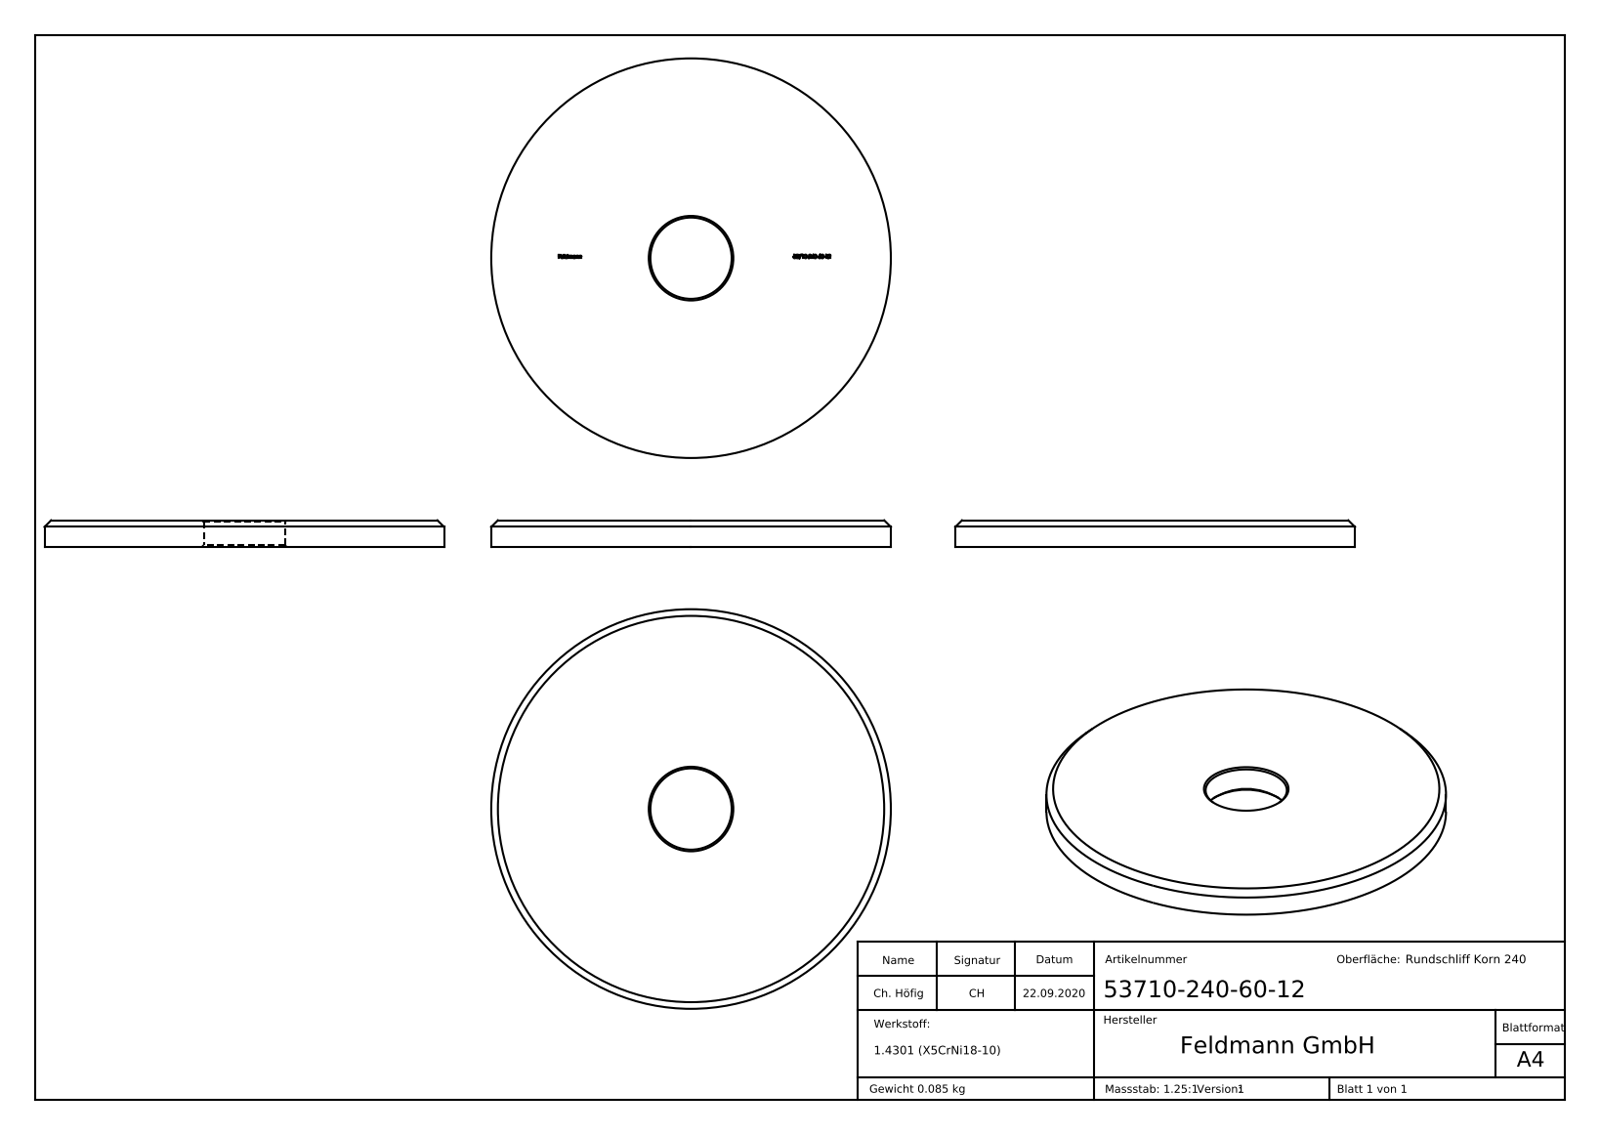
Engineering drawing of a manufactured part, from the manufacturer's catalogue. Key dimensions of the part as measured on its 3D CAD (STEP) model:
Part name (STEP PRODUCT): 53710-240-60-12
STEP written by: SolidWorks 2018 (CONFIG_CONTROL_DESIGN)
Units: millimetres
Bodies: 1 solid, 282 faces (154 planar, 4 cylindrical, 124 other)
Overall size (bounding box): 60 × 60 × 4
Volume: 10 746 mm³ · Surface area: 6 210 mm²
Round holes (diameter × count): ⌀12.2 ×1
Round bosses / shafts (diameter × count): ⌀60 ×1
Main face-to-face distances: 4, 3.9, 0.35, 0.53, 0.55, 0.5, 35.85, 39.43, 3.58, 0.81
